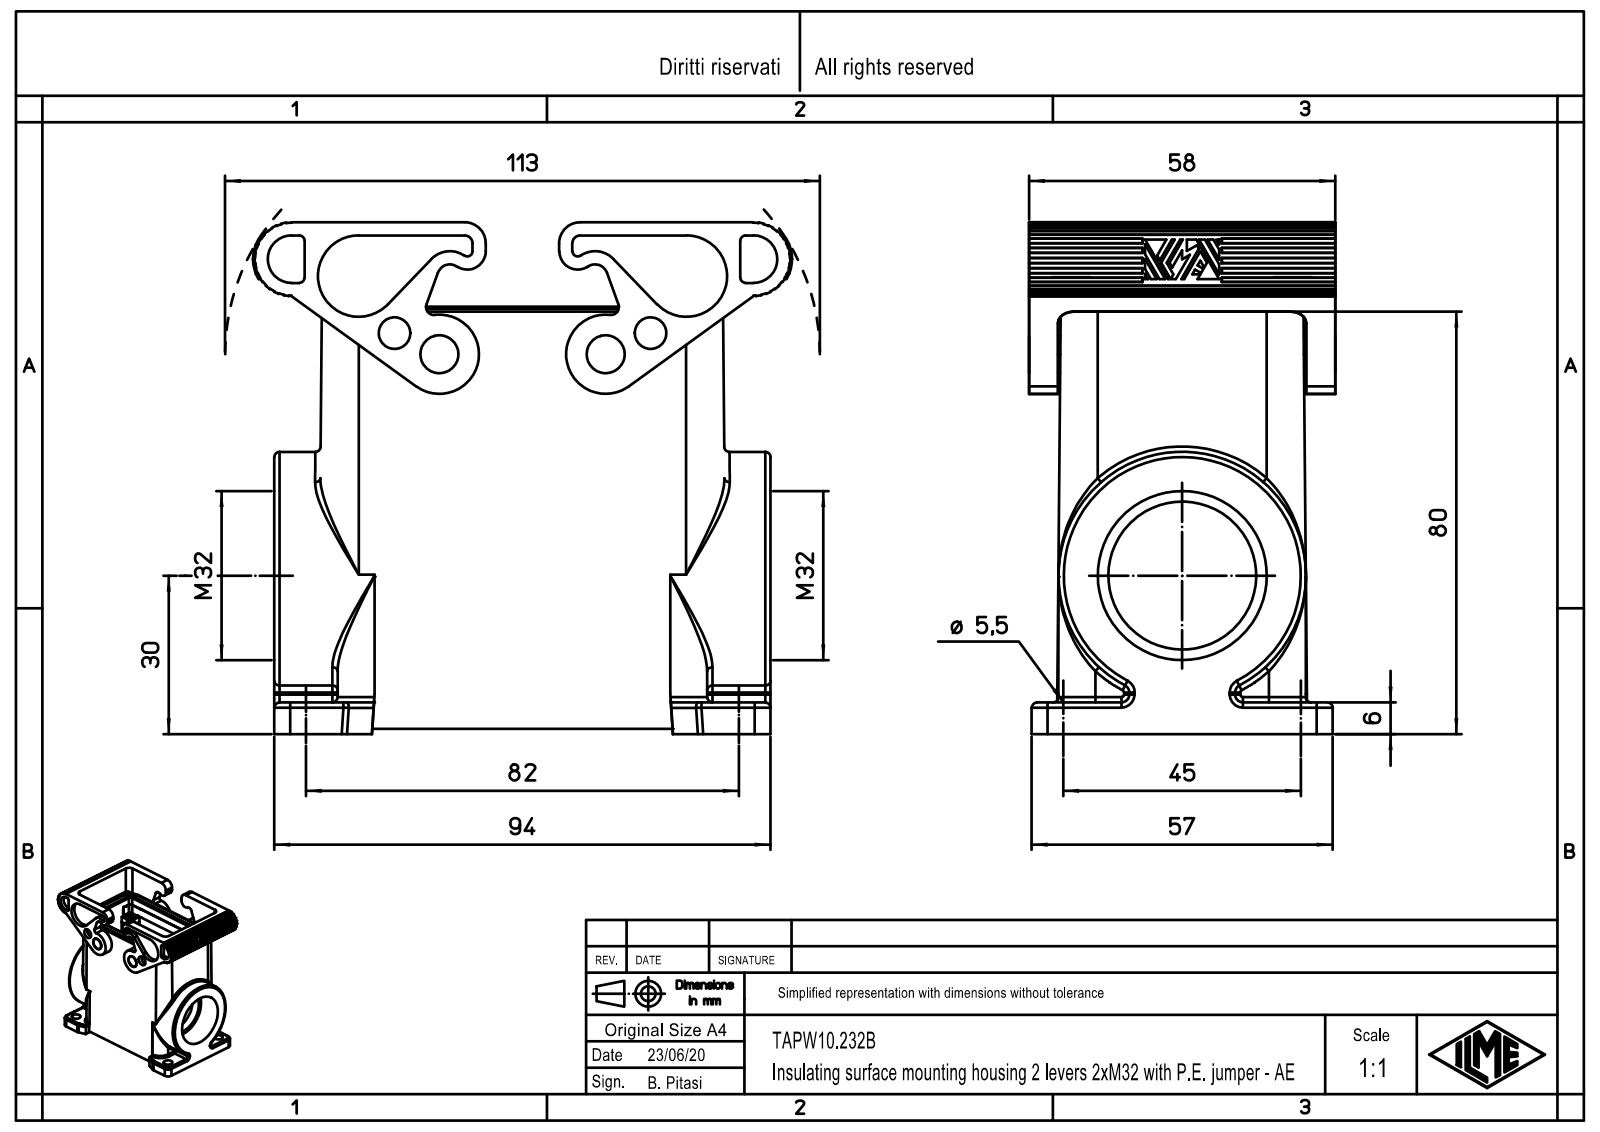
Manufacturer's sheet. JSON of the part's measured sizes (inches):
{"part_name": "TAPW10.232B", "step_written_by": "Creo Elements/Direct Modeling 20.1B 02-Apr-2019 (C) Parametric Technology GmbH (AUTOMOTIVE_DESIGN)", "units": "inches", "bodies": {"solids": 1, "faces": 944, "planar": 536, "cylindrical": 276, "other": 132}, "overall_size": [4.02, 3.815, 2.283], "volume_in3": 10.7, "surface_area_in2": 101.5, "round_holes": [[0.118, 4], [0.138, 4], [0.217, 4], [0.236, 2], [0.394, 2], [1.102, 1], [1.26, 1]], "round_bosses_or_shafts": [[0.189, 4], [0.276, 2], [1.845, 1]], "partial_cylinders_radius": [[0.039, 20], [0.059, 20], [0.118, 12], [0.138, 6], [0.276, 6], [0.02, 4], [0.051, 4], [0.063, 4]], "face_to_face_distances": [1.598, 0.217, 2.067, 0.039, 2.465, 0.098, 2.185, 0.256, 1.969, 0.118], "hole_center_spacings": [0.606, 1.5, 2.759, 3.081, 0.37, 1.063, 1.583, 1.772]}
